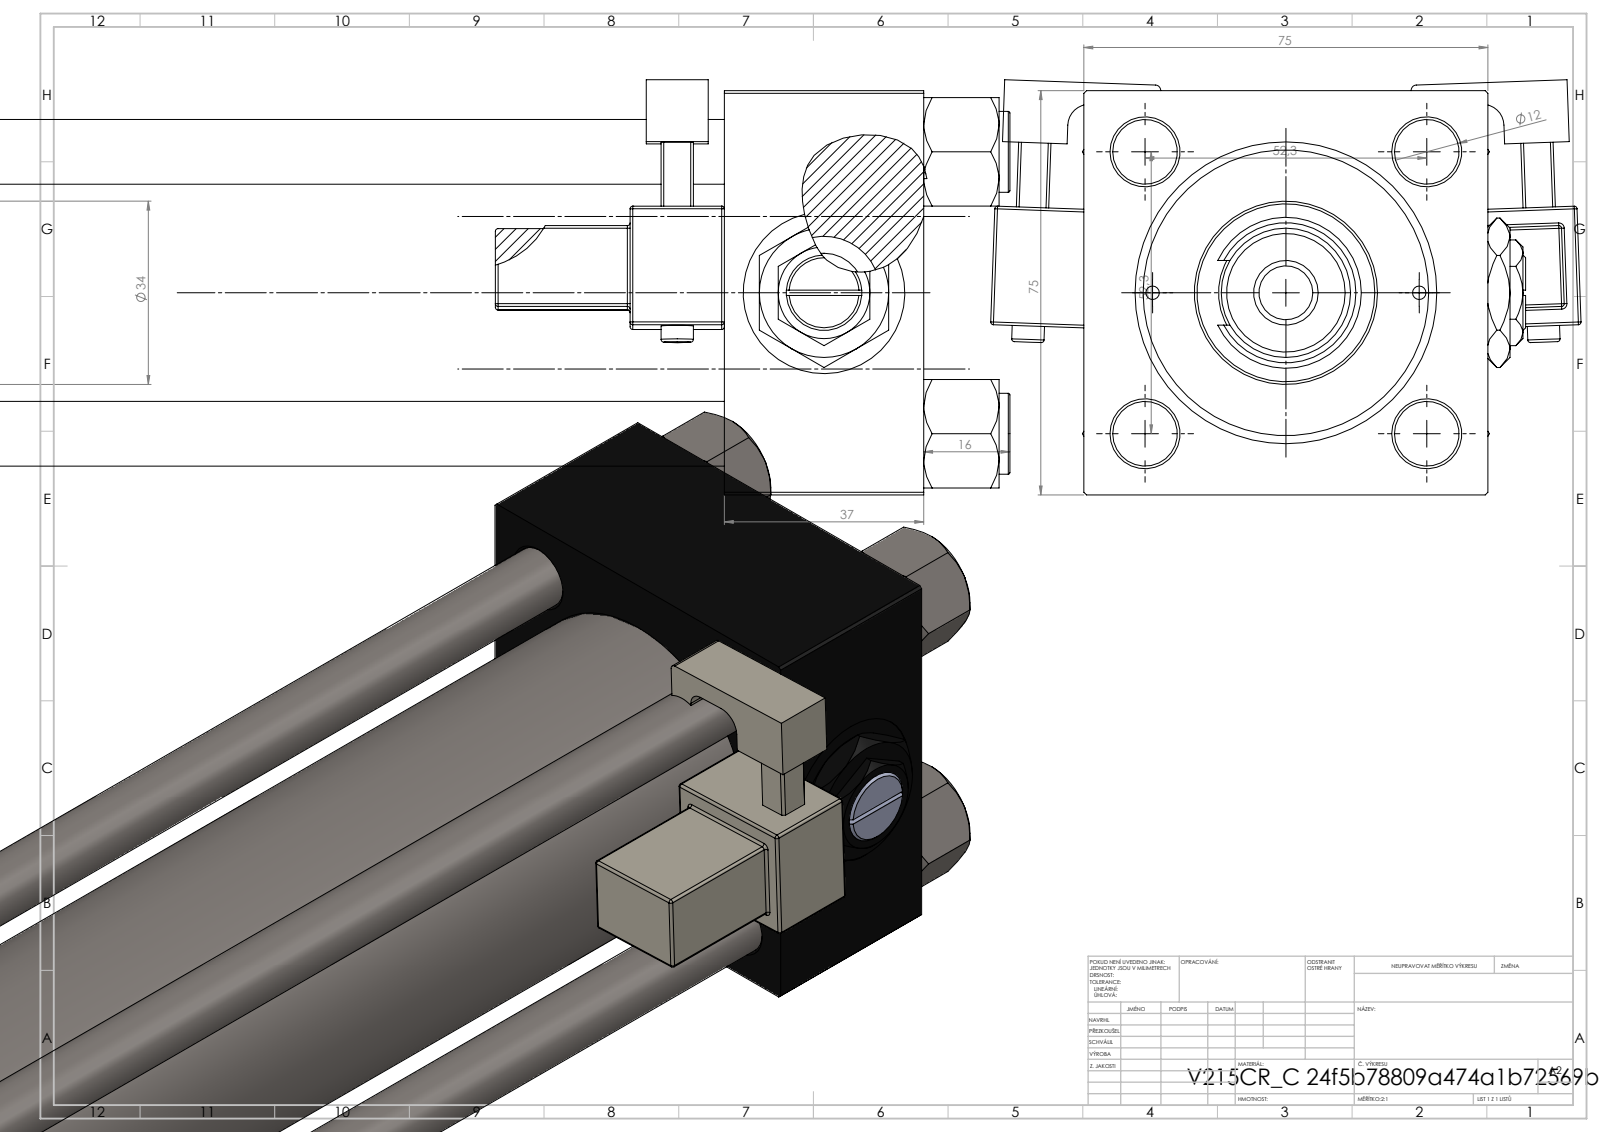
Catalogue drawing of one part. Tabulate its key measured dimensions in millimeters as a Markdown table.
| quantity | value |
| --- | --- |
| part name | V215CR_C_Body; V215CR_MSU; V215_VC_A; FEMALE_PART_FOR_DFA (+5 more) |
| STEP written by | SolidWorks 2019 (CONFIG_CONTROL_DESIGN) |
| units | millimeters |
| bodies | 17 solids, 1494 faces (661 planar, 175 cylindrical, 658 other) |
| overall size | 636 × 109.57 × 77.03 |
| volume | 1 217 000 mm³ |
| surface area | 381 341 mm² |
| round holes (diameter × count) | 12 × 4, 2.5 × 2, 7 × 2, 20.96 × 2, 30 × 2, 10.5 × 1, 22 × 1, 25 × 1, 41 × 1, 50 × 1, 53 × 1 |
| round bosses / shafts (diameter × count) | 15 × 4, 6 × 2, 56 × 1, 34 × 1, 28 × 1, 24 × 1, 18 × 1, 12 × 1 |
| partial cylindrical surfaces (radius × count) | 0.5 × 48, 1 × 2, 2.5 × 2, 4 × 2, 9.75 × 1, 10.5 × 1 |
| main face-to-face distances | 75, 37, 534, 497, 475, 438, 59, 505.3, 468.3, 30.3 |
| hole center spacings | 26.19, 36.98, 52.3, 57.22, 24.75, 73.96, 49.5, 473.5 |
